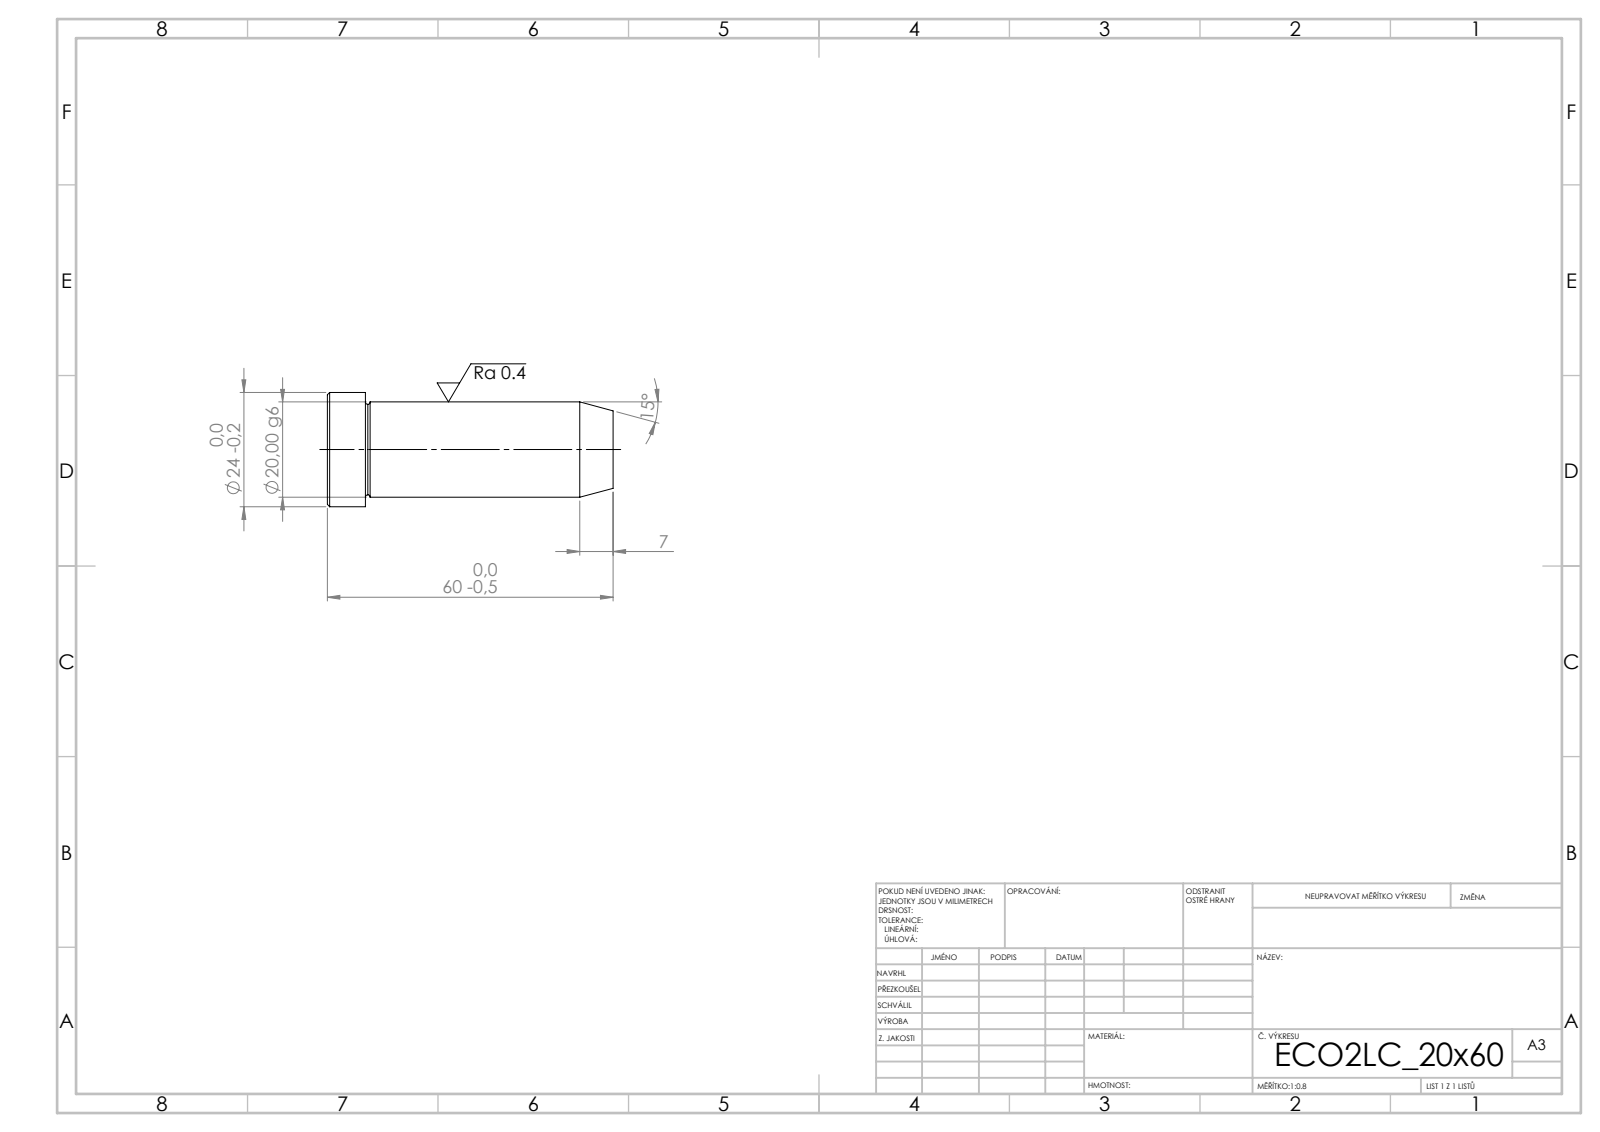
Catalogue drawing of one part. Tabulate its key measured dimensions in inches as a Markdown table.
| quantity | value |
| --- | --- |
| STEP written by | SolidWorks 2019 (CONFIG_CONTROL_DESIGN) |
| units | inches |
| bodies | 1 solid, 15 faces (3 planar, 4 cylindrical, 8 other) |
| overall size | 2.362 × 0.945 × 0.945 |
| volume | 1.192 in³ |
| surface area | 7.211 in² |
| round bosses / shafts (diameter × count) | 0.945 × 1, 0.787 × 1 |
| main face-to-face distances | 2.362, 2.047, 0.315 |
